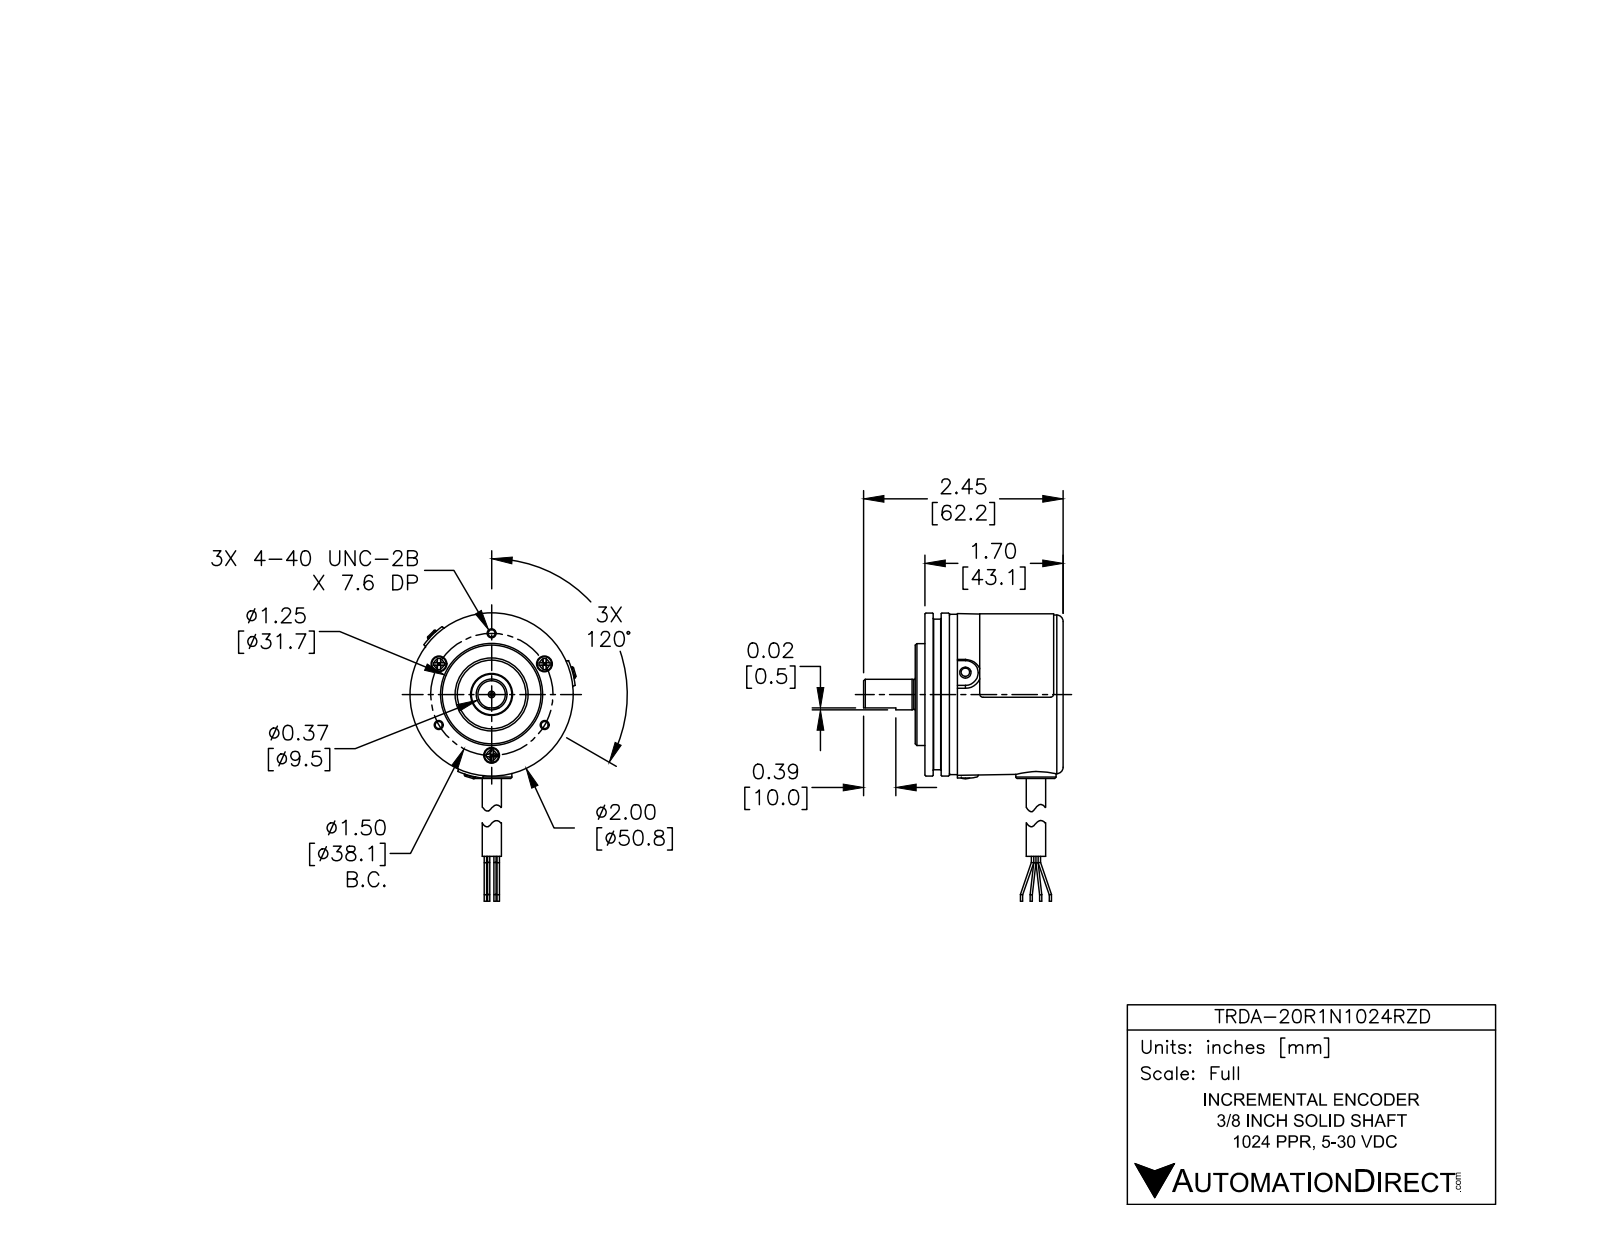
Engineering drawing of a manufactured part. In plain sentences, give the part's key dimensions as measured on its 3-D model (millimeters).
The part is named "TRDA-20R1N1000RZD". Its 3-D file was written by "SolidWorks 2017 (AUTOMOTIVE_DESIGN)". It is 1 solid with 243 faces: 71 planar, 79 cylindrical and 93 other. Overall it measures 153.4 by 62.2 by 51.4 millimeters. Its volume is 90 190 cubic millimeters and its surface area 17 370 square millimeters. Round holes: 3 of diameter 2.3, 3 of diameter 2.3, 3 of diameter 4.5, 1 of diameter 1.2, 1 of diameter 7, 1 of diameter 22, 1 of diameter 22.1, 1 of diameter 32. Round bosses or shafts: 3 of diameter 2, 2 of diameter 6, 1 of diameter 50.8, 1 of diameter 50, 1 of diameter 47, 1 of diameter 31.8, 1 of diameter 13, 1 of diameter 12.5. Partial cylindrical surfaces (rounded edges, fillets, slot ends): 12 of radius 0.5, 3 of radius 4, 1 of radius 24.2, 1 of radius 26.2. The main face-to-face distances are 43.1, 2.5, 46.1, 3, 1, 42.1, 4, 40.6, 1.5, 5.5. The hole center spacings are 19, 19, 19.1, 33, 38, 19, 32.9, 32.9.
